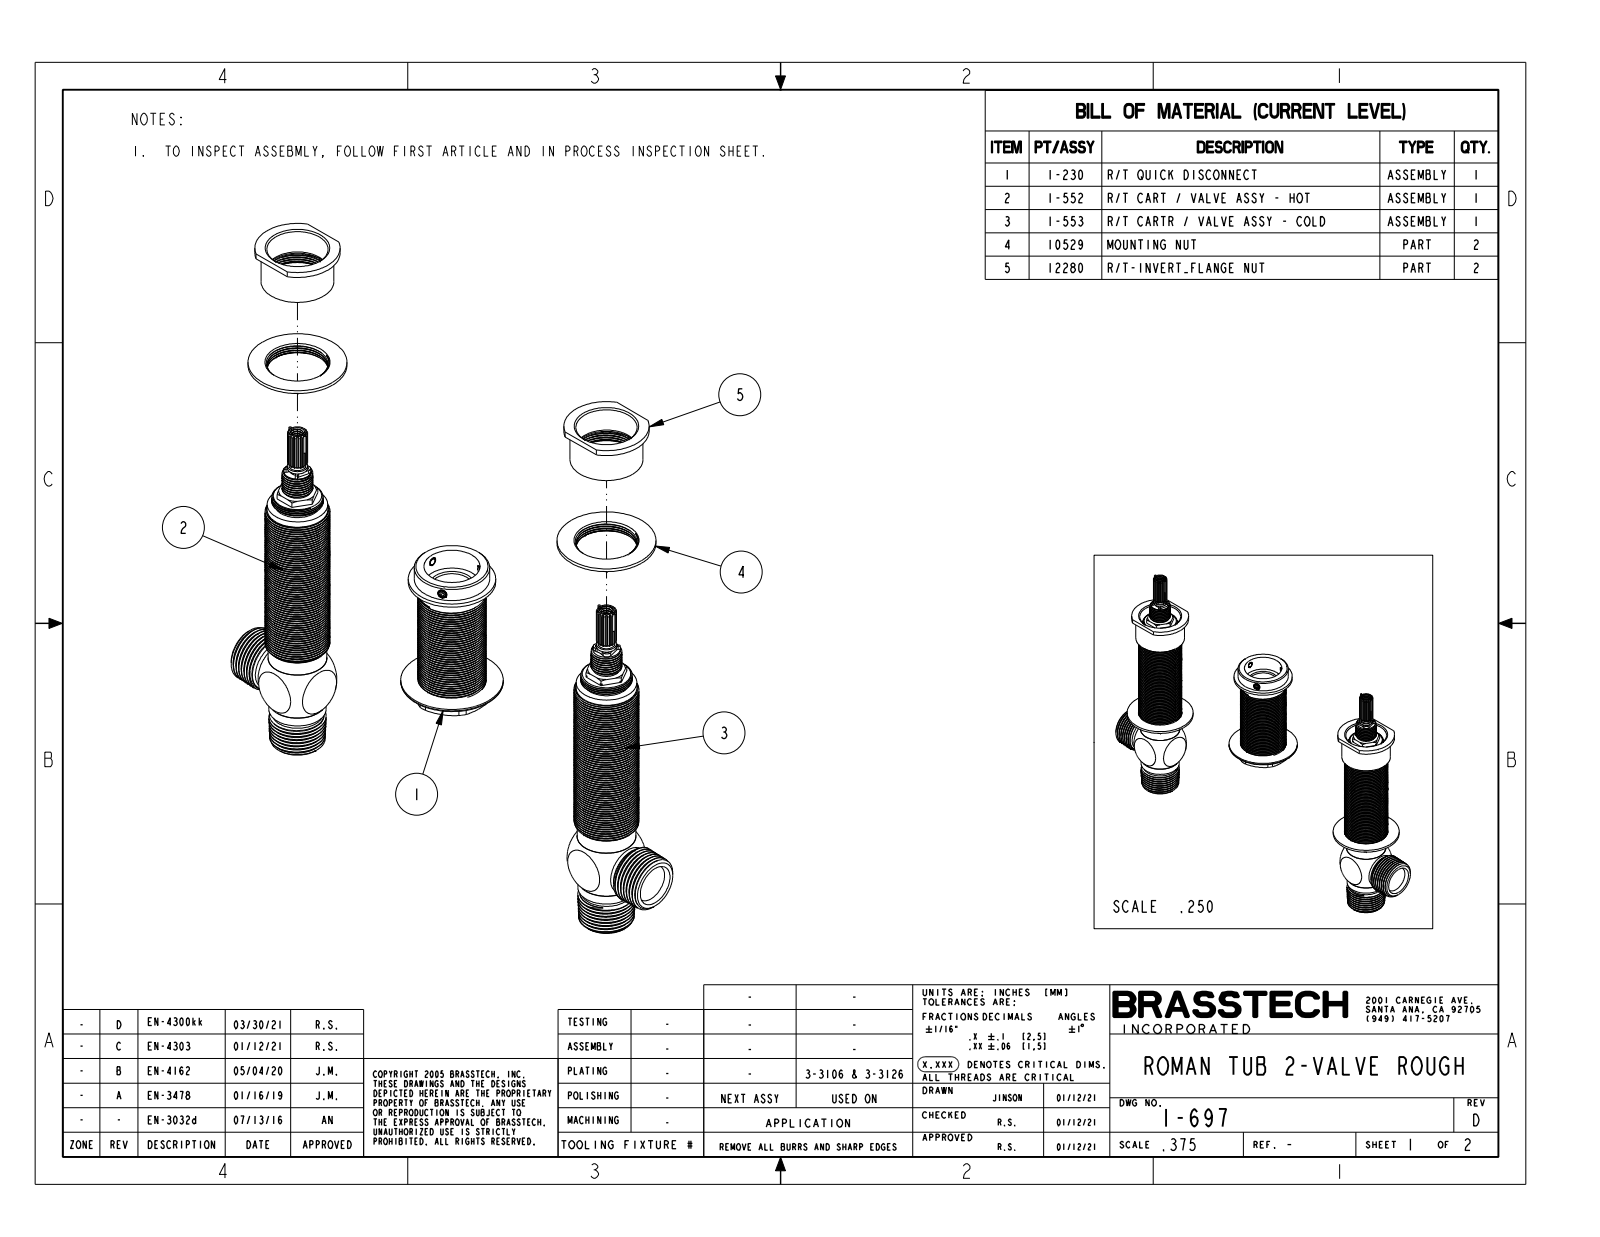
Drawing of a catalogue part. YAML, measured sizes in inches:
part_name: "1-697"
step_written_by: "CREO PARAMETRIC BY PTC INC, 2018400 (AUTOMOTIVE_DESIGN)"
units: inches
bodies: {solids: 4, faces: 1296, planar: 259, cylindrical: 553, other: 484}
overall_size: [10.52, 6.941, 1.875]
volume: 16.45
surface_area: 122.9
round_holes:
  - {diameter: 0.196, count: 2}
  - {diameter: 0.201, count: 2}
  - {diameter: 1.12, count: 2}
  - {diameter: 1.18, count: 2}
  - {diameter: 0.136, count: 1}
  - {diameter: 0.709, count: 1}
  - {diameter: 1.025, count: 1}
round_bosses_or_shafts:
  - {diameter: 1.811, count: 2}
  - {diameter: 1.335, count: 2}
  - {diameter: 1.187, count: 2}
  - {diameter: 1.11, count: 2}
  - {diameter: 1.075, count: 2}
  - {diameter: 1.047, count: 2}
  - {diameter: 0.945, count: 2}
  - {diameter: 0.929, count: 2}
partial_cylinders:
  - {radius: 0.04, count: 8}
  - {radius: 0.08, count: 8}
  - {radius: 0.164, count: 2}
  - {radius: 0.26, count: 2}
  - {radius: 0.3, count: 2}
  - {radius: 0.775, count: 2}
  - {radius: 0.78, count: 2}
  - {radius: 0.598, count: 1}
face_to_face_distances: [2.2, 0.061, 1.011, 0.95, 3.211, 3.15, 0.062, 3.321, 3.26, 2.31]
hole_center_spacings: [4, 4.388, 8]
